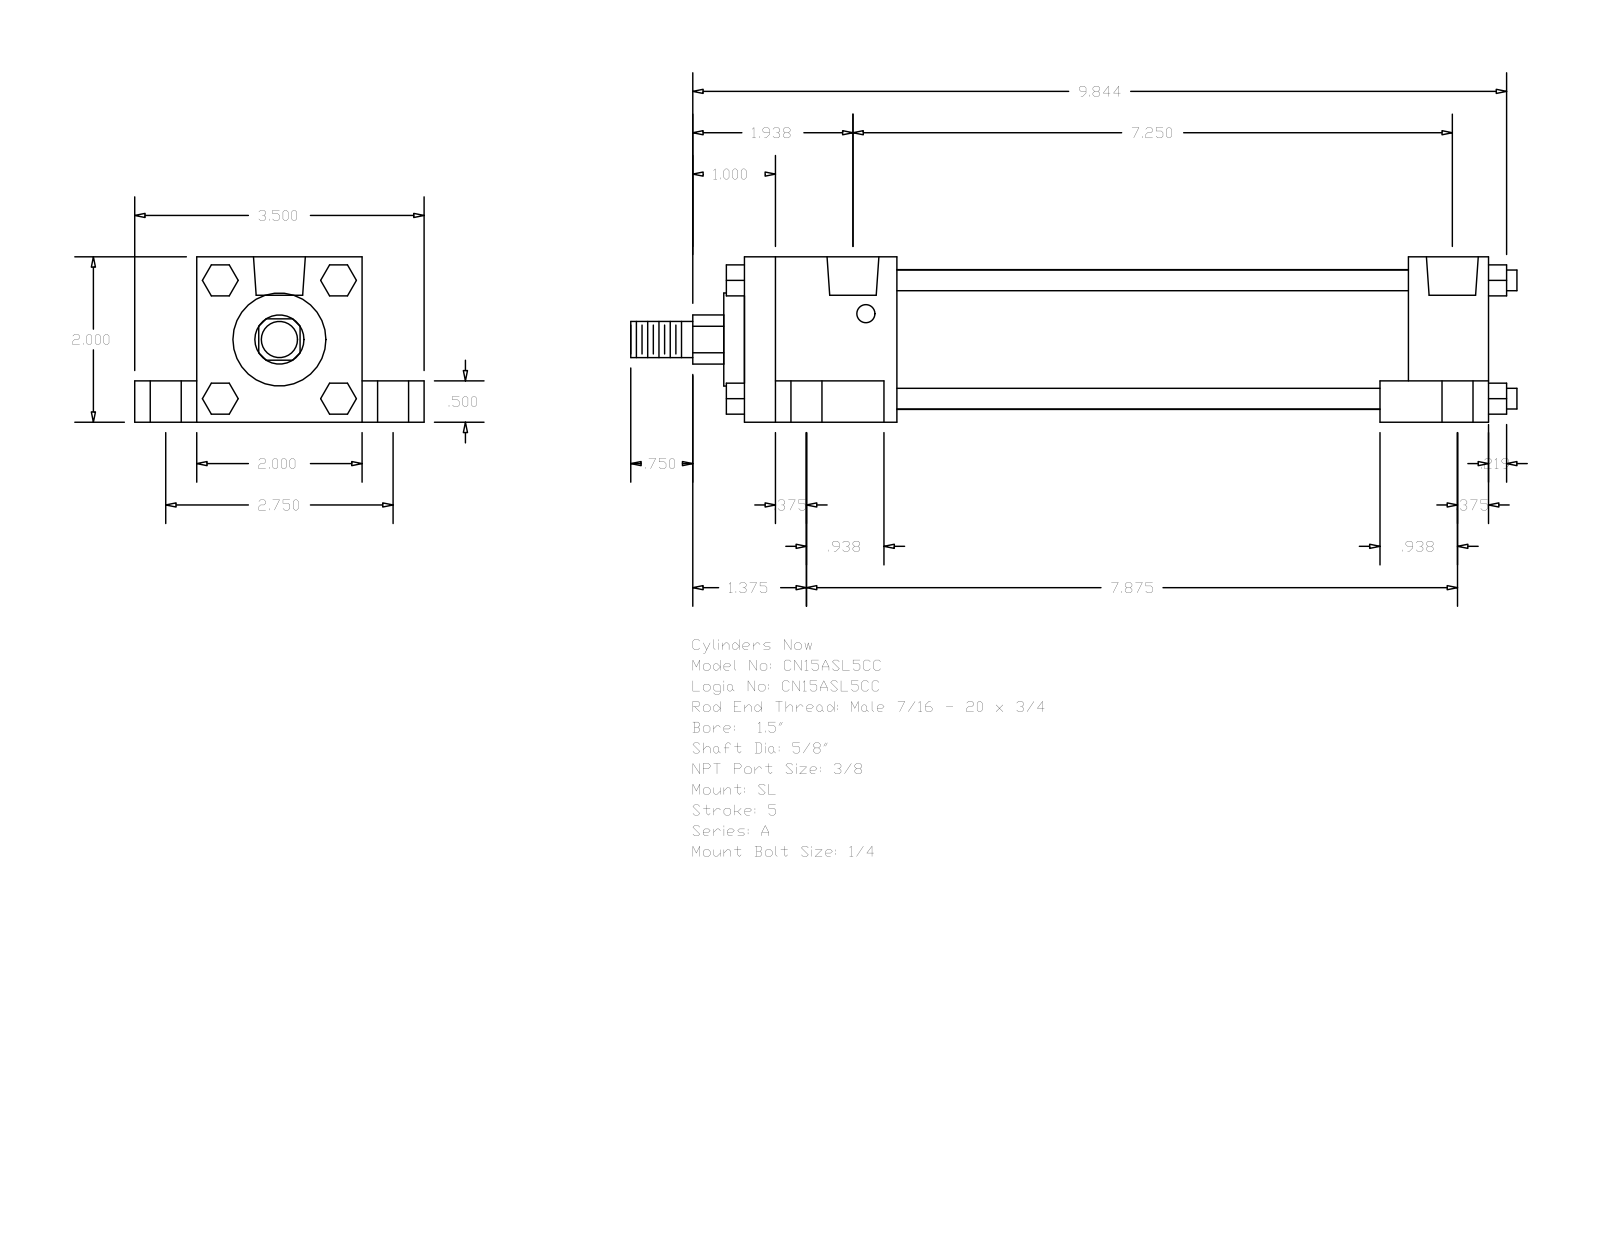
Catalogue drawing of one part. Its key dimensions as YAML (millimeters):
part_name: "A_SL__0150_0.625"
step_written_by: "GSSL Pune (CONFIG_CONTROL_DESIGN)"
units: millimeters
bodies: {solids: 0, faces: 148, planar: 112, cylindrical: 36, other: 0}
overall_size: [272.26, 88.9, 50.8]
round_holes:
  - {diameter: 5.56, count: 4}
  - {diameter: 9.53, count: 4}
  - {diameter: 15.88, count: 4}
  - {diameter: 15.93, count: 2}
round_bosses_or_shafts:
  - {diameter: 6.35, count: 4}
  - {diameter: 42.93, count: 1}
  - {diameter: 28.57, count: 1}
  - {diameter: 15.88, count: 1}
  - {diameter: 11.11, count: 1}
partial_cylinders:
  - {radius: 7.54, count: 1}
face_to_face_distances: [50.8, 19.05, 38.1, 12.7, 69.85, 228.59, 9.52, 203.99, 24.6, 46.83]
hole_center_spacings: [3.97, 34.96, 35.36, 37.73, 39.41, 69.84, 176.21, 180.18]
